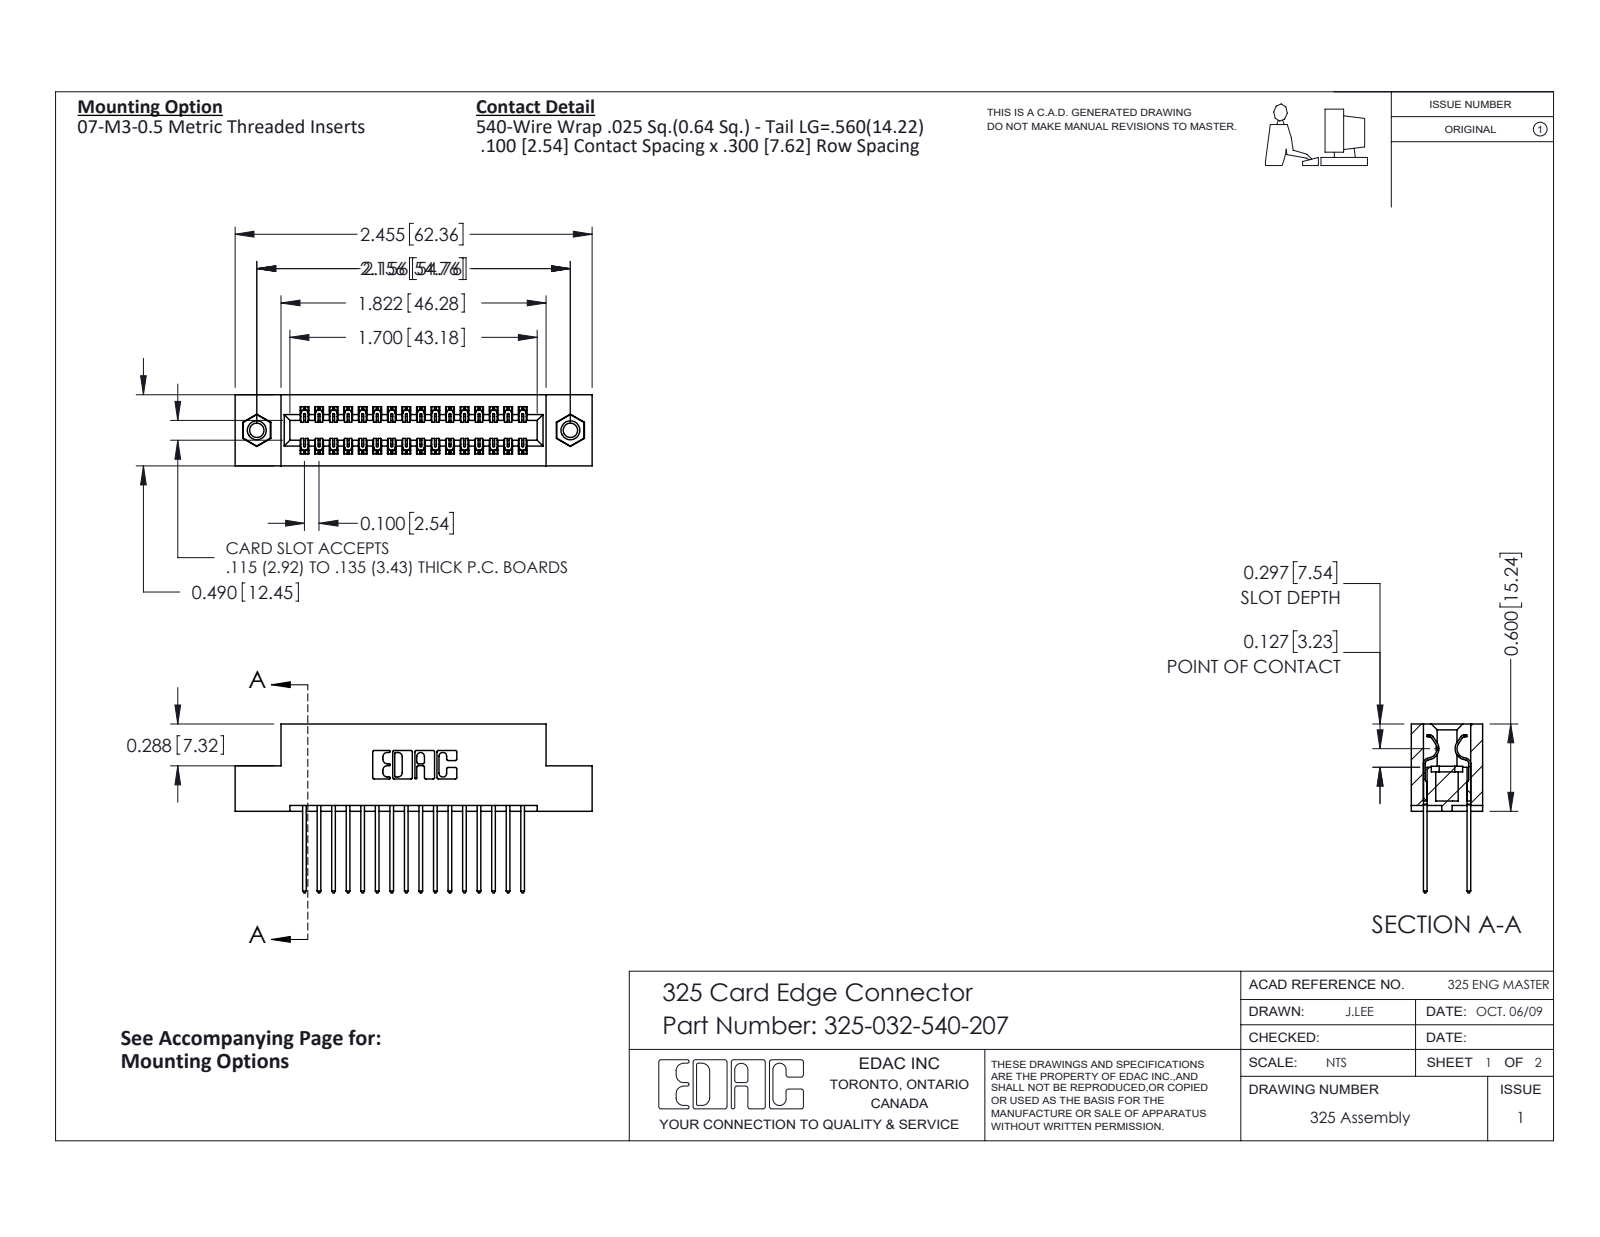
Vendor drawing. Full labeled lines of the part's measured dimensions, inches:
Part name (STEP PRODUCT): 325-032-540-207; 345-250-001_345-250-005-103; 325 Part_TI; 325-292-001_325-293-140
STEP written by: SolidWorks 2016 (CONFIG_CONTROL_DESIGN)
Units: inches
Bodies: 35 solids, 1838 faces (1254 planar, 568 cylindrical, 16 other)
Overall size (bounding box): 2.455 × 1.16 × 0.49
Volume: 0.484 in³ · Surface area: 14.85 in²
Round holes (diameter × count): ⌀0.098 ×2, ⌀0.125 ×2, ⌀0.16 ×2
Round bosses / shafts (diameter × count): ⌀0.155 ×2
Partial cylindrical surfaces — rounded edges, fillets, slot ends (radius × count): R0.006 ×48, R0.01 ×32, R0.01 ×22, R0.007 ×6, R0.031 ×6, R0.026 ×3, R0.014 ×2, R0.022 ×2
Main face-to-face distances: 0.083, 0.407, 0.3, 0.107, 0.383, 0.025, 0.49, 0.325, 0.04, 0.6
Hole centre spacings: 2.156
